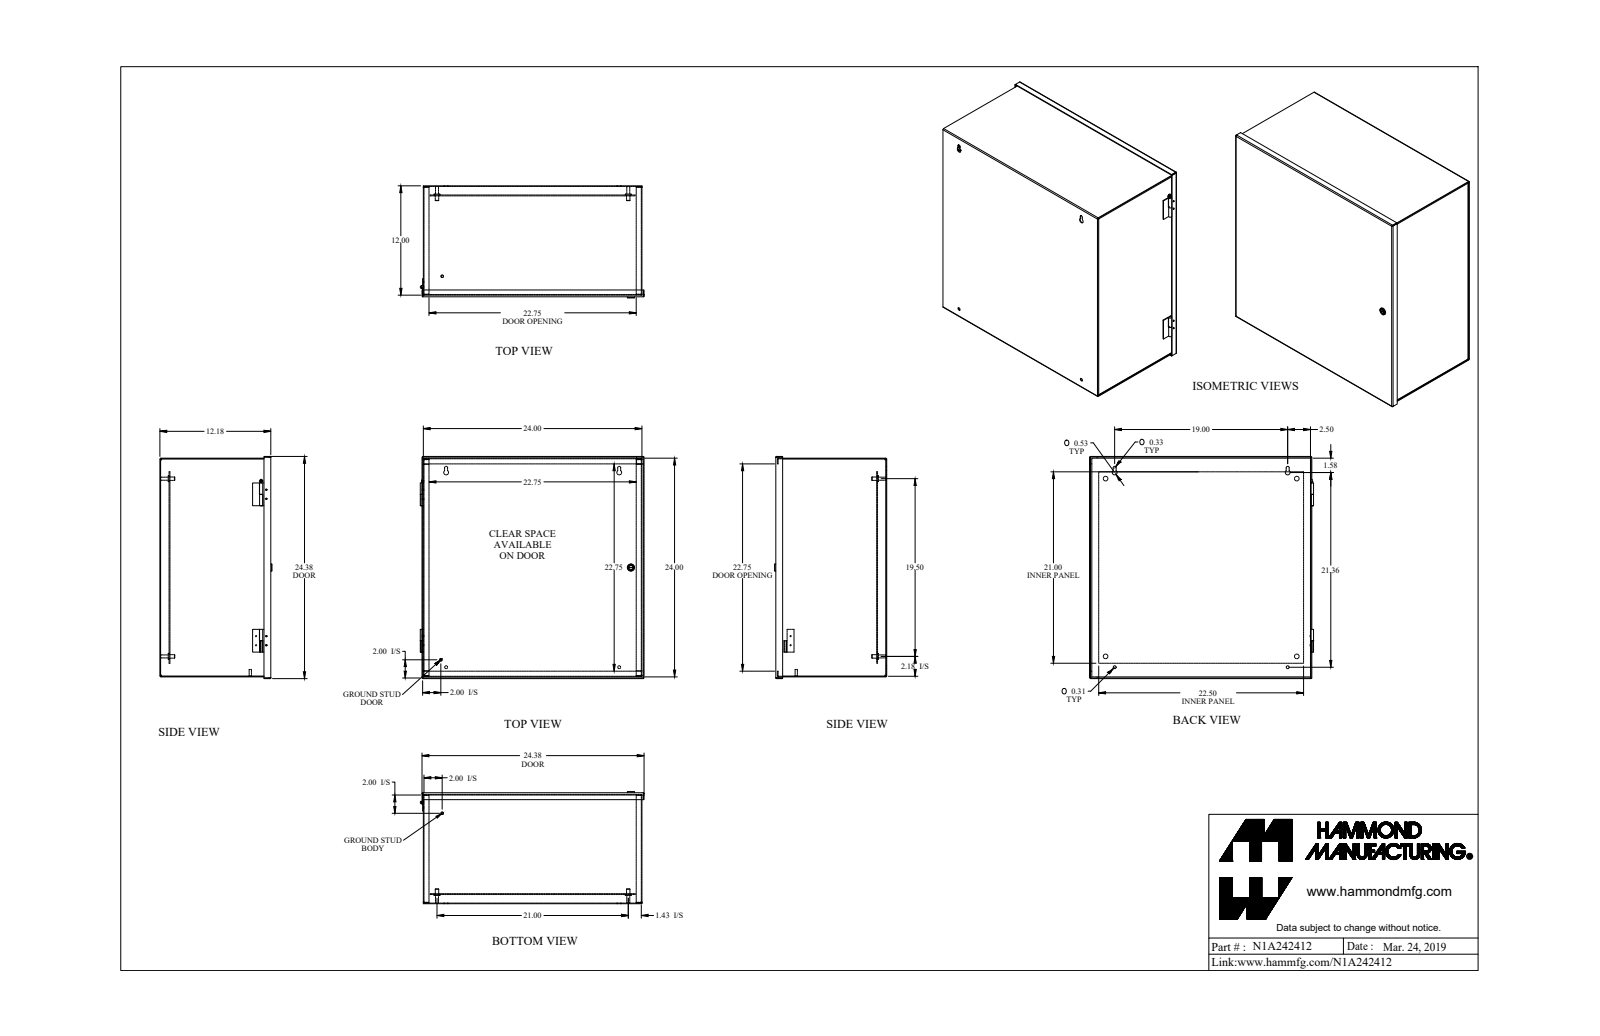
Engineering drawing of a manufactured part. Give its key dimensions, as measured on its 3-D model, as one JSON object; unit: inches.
{"part_name": "N1A242412", "step_written_by": "SolidWorks 2018 (AUTOMOTIVE_DESIGN)", "units": "inches", "bodies": {"solids": 23, "faces": 520, "planar": 294, "cylindrical": 182, "other": 44}, "overall_size": [24.574, 24.384, 12.299], "volume_in3": 225.1, "surface_area_in2": 5973, "round_holes": [[0.14, 8], [0.5, 4], [0.307, 2], [0.312, 2], [0.445, 2], [0.17, 1], [0.187, 1], [0.516, 1]], "round_bosses_or_shafts": [[0.128, 8], [0.375, 5], [0.65, 4], [0.33, 4], [1, 2], [0.281, 2], [0.25, 2], [0.788, 1]], "partial_cylinders_radius": [[0.036, 16], [0.108, 16], [0.06, 2], [0.153, 2], [0.164, 2], [0.266, 2], [0.03, 1], [0.125, 1]], "face_to_face_distances": [0.072, 12.105, 23.928, 12.033, 12.177, 24, 23.856, 1.104, 1.032, 11.001], "hole_center_spacings": [1, 1.119, 1.553, 2.031, 9.754, 16.062, 16.062, 16.1]}
